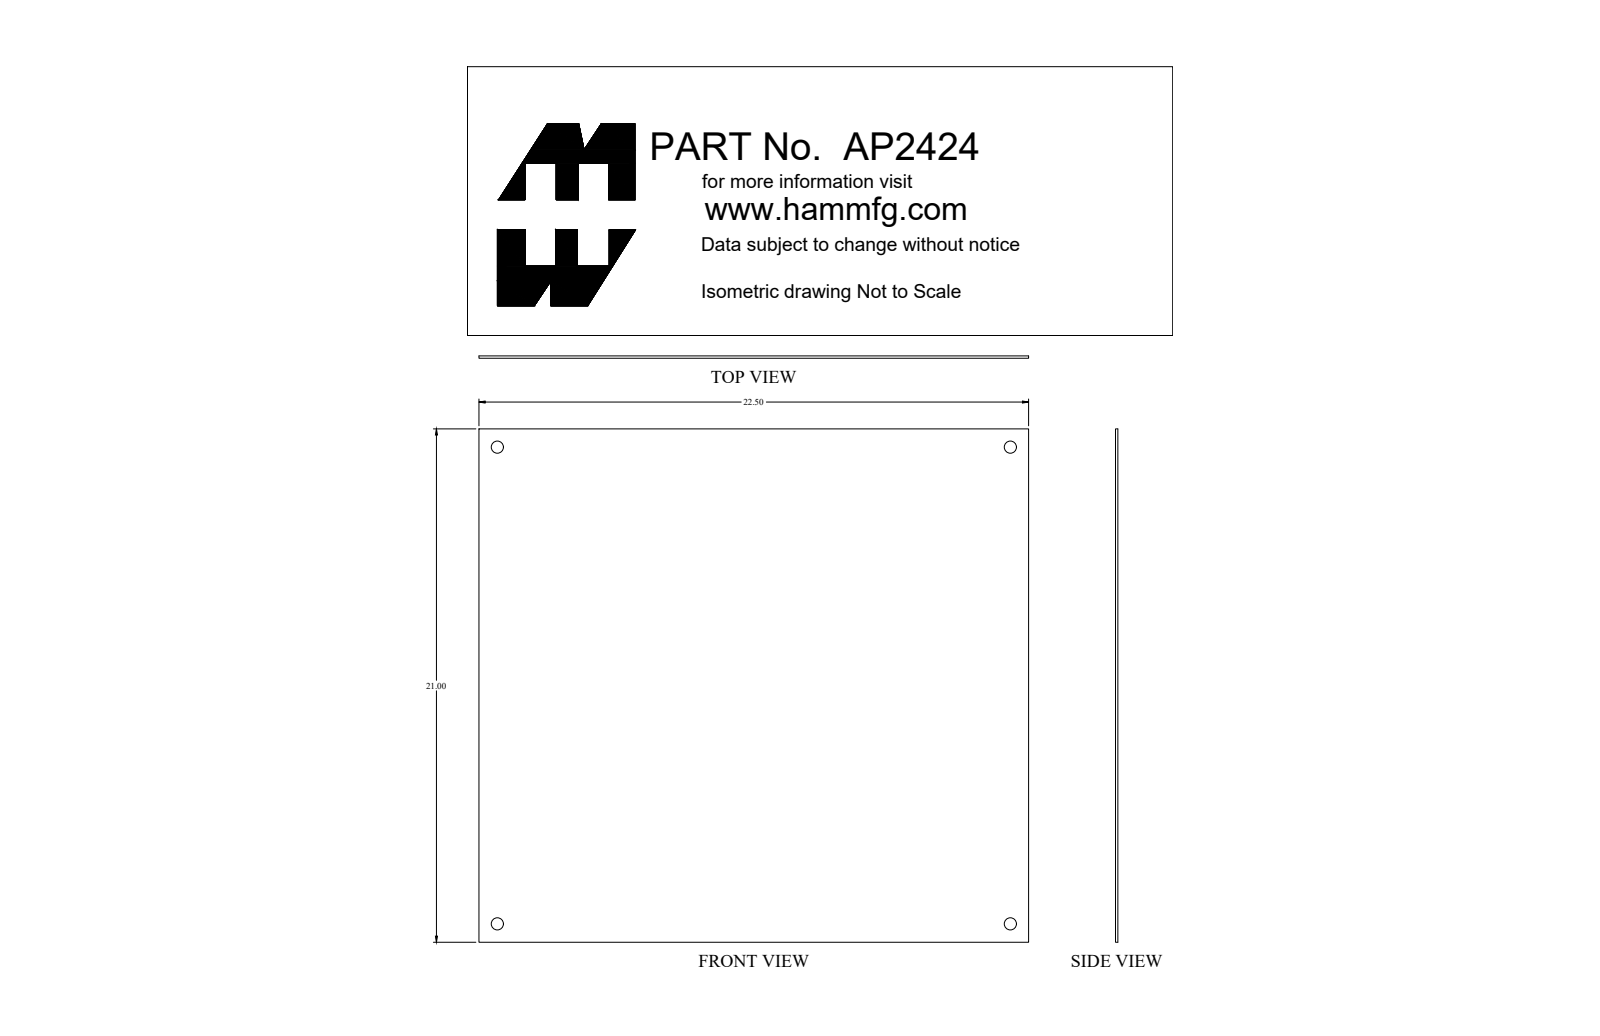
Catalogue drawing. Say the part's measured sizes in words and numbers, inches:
The part is named "AP2424_Default". Its 3-D file was written by "SolidWorks 2019 (CONFIG_CONTROL_DESIGN)". It is 1 solid with 14 faces: 6 planar, 8 cylindrical and 0 other. Overall it measures 22.5 by 21 by 0.095 inches. Its volume is 44.81 cubic inches and its surface area 952.3 square inches. Round holes: 4 of diameter 0.5. The main face-to-face distances are 0.095, 21, 22.5. The hole center spacings are 19.5, 21, 28.657.
